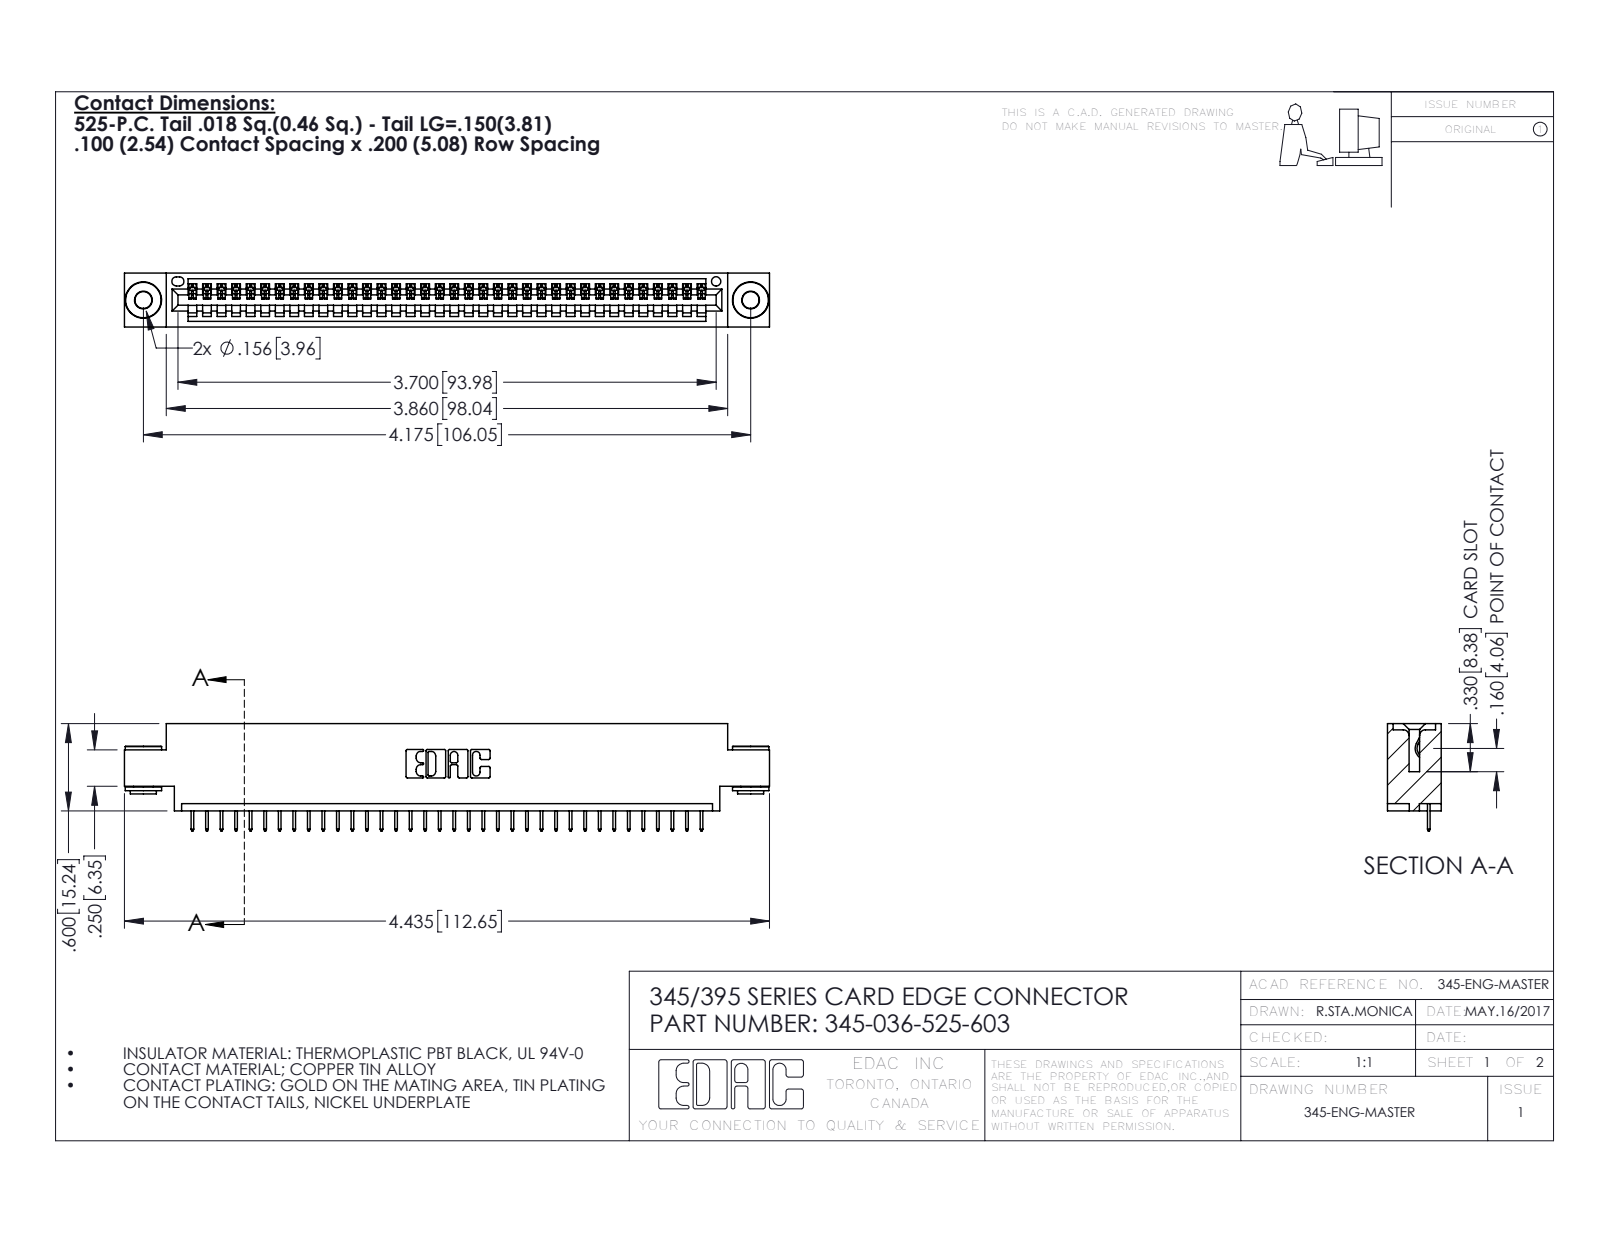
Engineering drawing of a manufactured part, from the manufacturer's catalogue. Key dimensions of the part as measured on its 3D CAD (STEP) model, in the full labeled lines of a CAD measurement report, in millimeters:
Part name (STEP PRODUCT): 345-292-001_345-293-125; 345-250-002_345-250-002-102; 345-036-525-603; 345 Part_0.170 Offset - 0.156 Dia-TH
STEP written by: SolidWorks 2020 (CONFIG_CONTROL_DESIGN)
Units: millimetres
Bodies: 39 solids, 2400 faces (1750 planar, 642 cylindrical, 8 other)
Overall size (bounding box): 112.6 × 18.7 × 9.4
Volume: 10 400 mm³ · Surface area: 13 600 mm²
Round holes (diameter × count): ⌀2.9 ×2, ⌀4 ×2, ⌀1.6 ×1
Round bosses / shafts (diameter × count): ⌀6.4 ×2, ⌀4.6 ×2, ⌀3.5 ×2
Partial cylindrical surfaces — rounded edges, fillets, slot ends (radius × count): R0.2 ×72, R0.3 ×22, R0.2 ×6, R0.8 ×6, R0.7 ×3, R0.8 ×2, R1 ×2, R0.4 ×1
Main face-to-face distances: 1.8, 7.6, 9.4, 5.1, 2.5, 6.9, 0.6, 5.7, 4.4, 1.8
Hole centre spacings: 6.9, 100.1, 106
